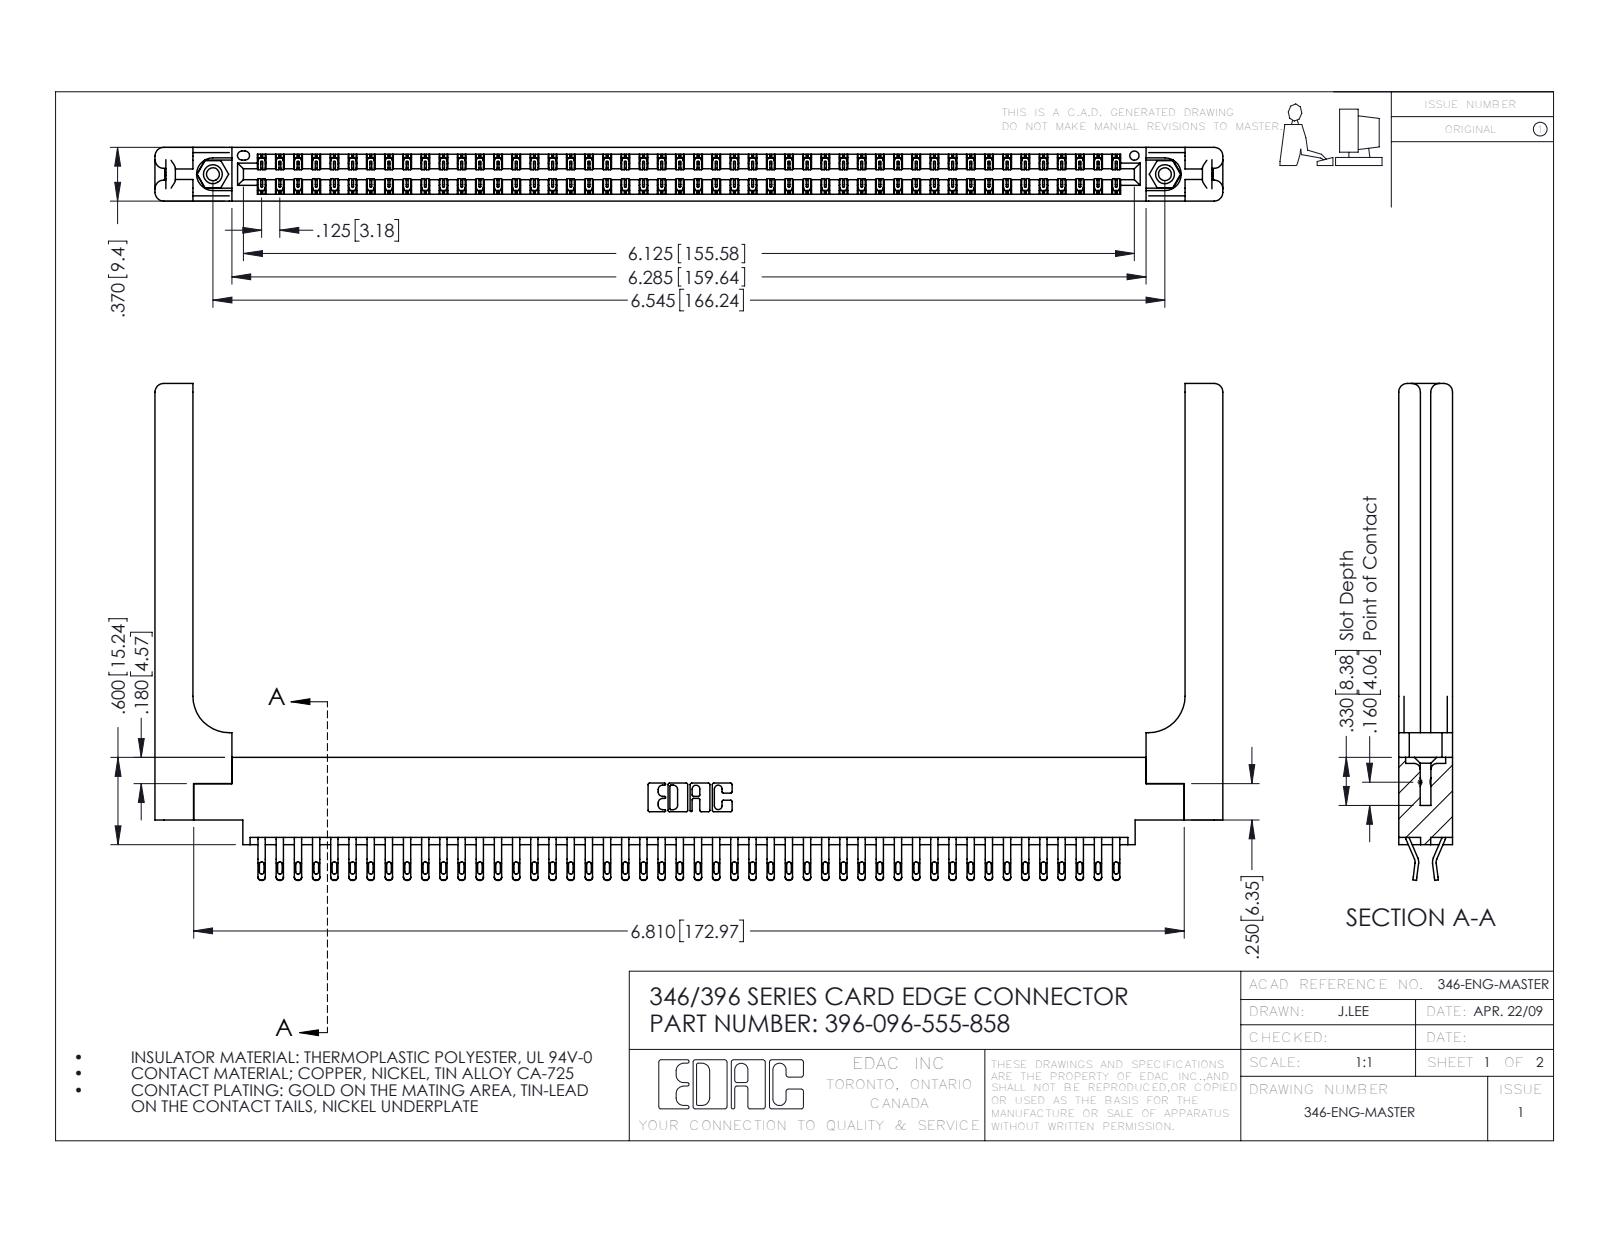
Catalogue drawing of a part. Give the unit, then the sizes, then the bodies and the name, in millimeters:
Units: millimetres
Overall size (bounding box): 186.5 × 86.7 × 9.4
Round holes (diameter × count): ⌀2.3 ×2, ⌀3.2 ×2, ⌀4 ×2, ⌀1.6 ×1
Round bosses / shafts (diameter × count): ⌀3.9 ×2
Partial cylindrical surfaces — rounded edges, fillets, slot ends (radius × count): R0.4 ×192, R0.5 ×192, R0.2 ×144, R0.3 ×22, R1.5 ×16, R0.2 ×6, R0.8 ×6, R0.7 ×3
Main face-to-face distances: 9.4, 1.2, 8.2, 1.8, 3.8, 3.8, 6.4, 0.6, 7.6, 7
Hole centre spacings: 6.2, 160.9, 166.2
Volume: 25 840 mm³ · Surface area: 31 460 mm²
Bodies: 101 solids, 5950 faces (3396 planar, 2494 cylindrical, 60 other)
Part name (STEP PRODUCT): 346-220-058_345-220-058; 396-096-555-858; 346 Part_0.170 Offset - 0.156 Dia-TH; 345-250-001_345-250-001-102 (+1 more)
STEP written by: SolidWorks 2016 (CONFIG_CONTROL_DESIGN)
